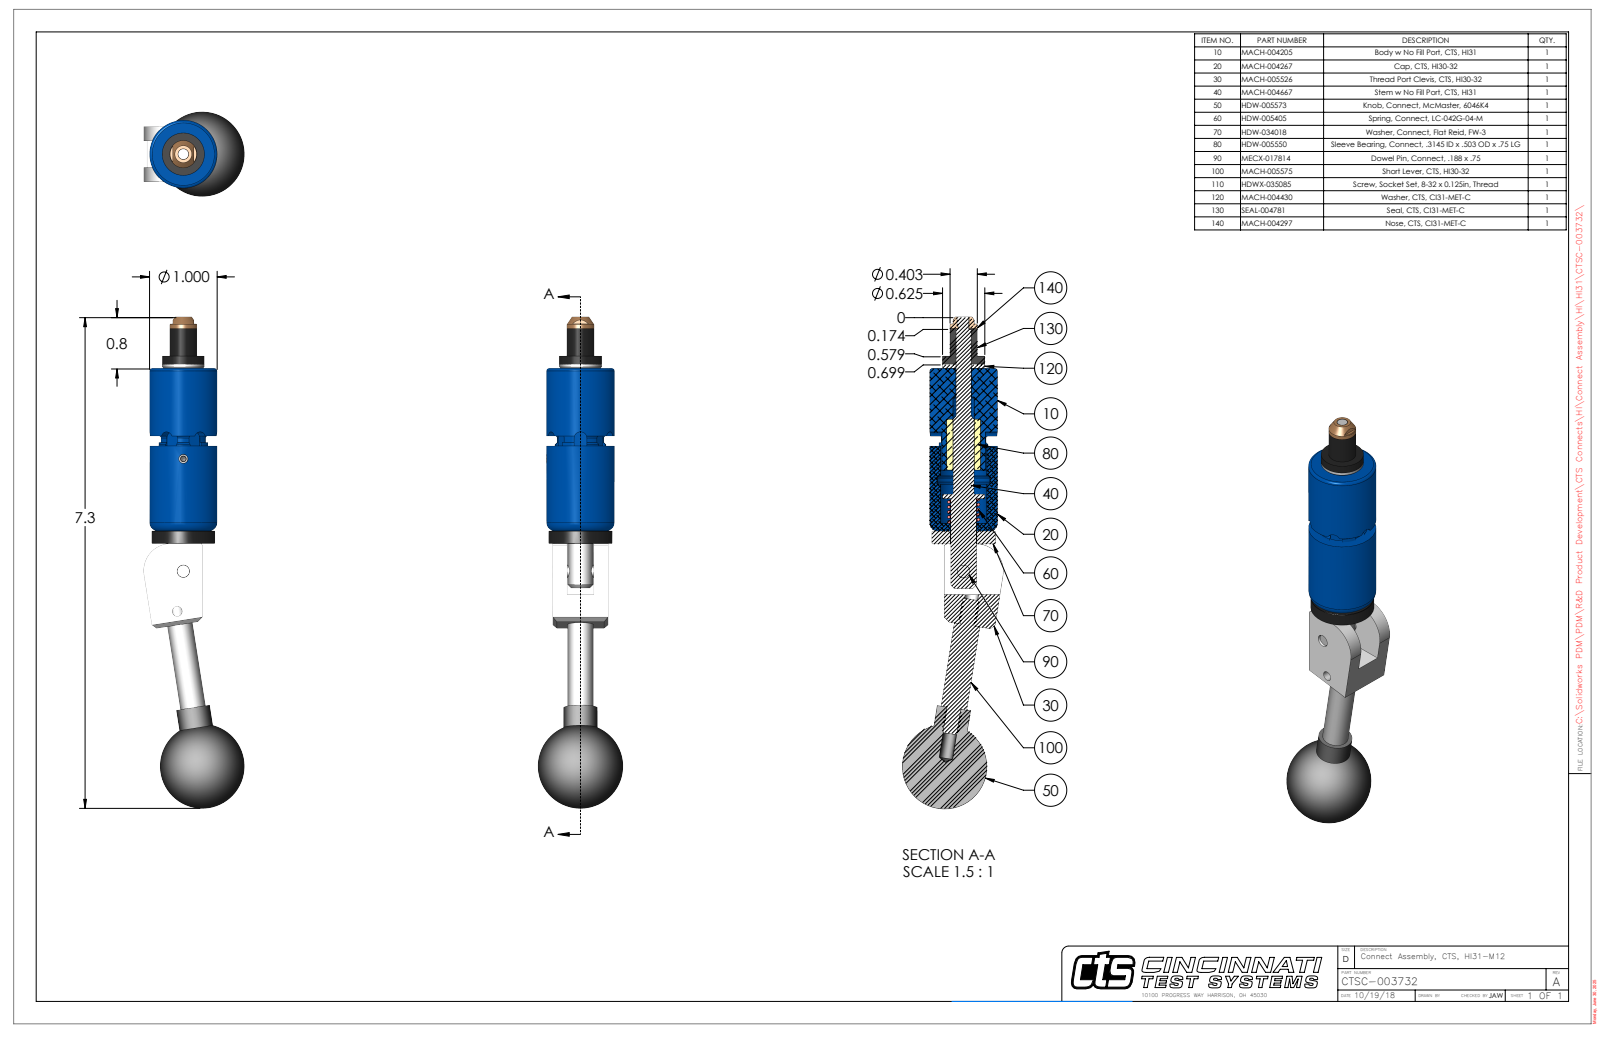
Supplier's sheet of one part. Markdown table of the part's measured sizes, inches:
| quantity | value |
| --- | --- |
| part name | CTSC-003732 |
| STEP written by | SolidWorks 2023 (AUTOMOTIVE_DESIGN) |
| units | inches |
| bodies | 9 solids, 268 faces (101 planar, 109 cylindrical, 58 other) |
| overall size | 7.256 × 1.492 × 1.25 |
| volume | 3.865 in³ |
| surface area | 31.39 in² |
| round holes (diameter × count) | 0.201 × 2, 0.136 × 1, 0.15 × 1, 0.159 × 1, 0.189 × 1, 0.218 × 1, 0.228 × 1, 0.229 × 1, 0.385 × 1, 0.392 × 1, 0.688 × 1 |
| round bosses / shafts (diameter × count) | 1 × 1, 0.936 × 1, 0.625 × 1, 0.5 × 1, 0.403 × 1, 0.38 × 1, 0.375 × 1, 0.25 × 1 |
| partial cylindrical surfaces (radius × count) | 0.093 × 6, 0.029 × 2, 0.375 × 1, 0.4 × 1, 0.467 × 1 |
| main face-to-face distances | 0.21, 0.602, 0.812, 2.4, 2.587, 0.187, 0.391, 0.06, 2.46, 2.647 |
| hole center spacings | 0.599, 1.658, 2.252 |
